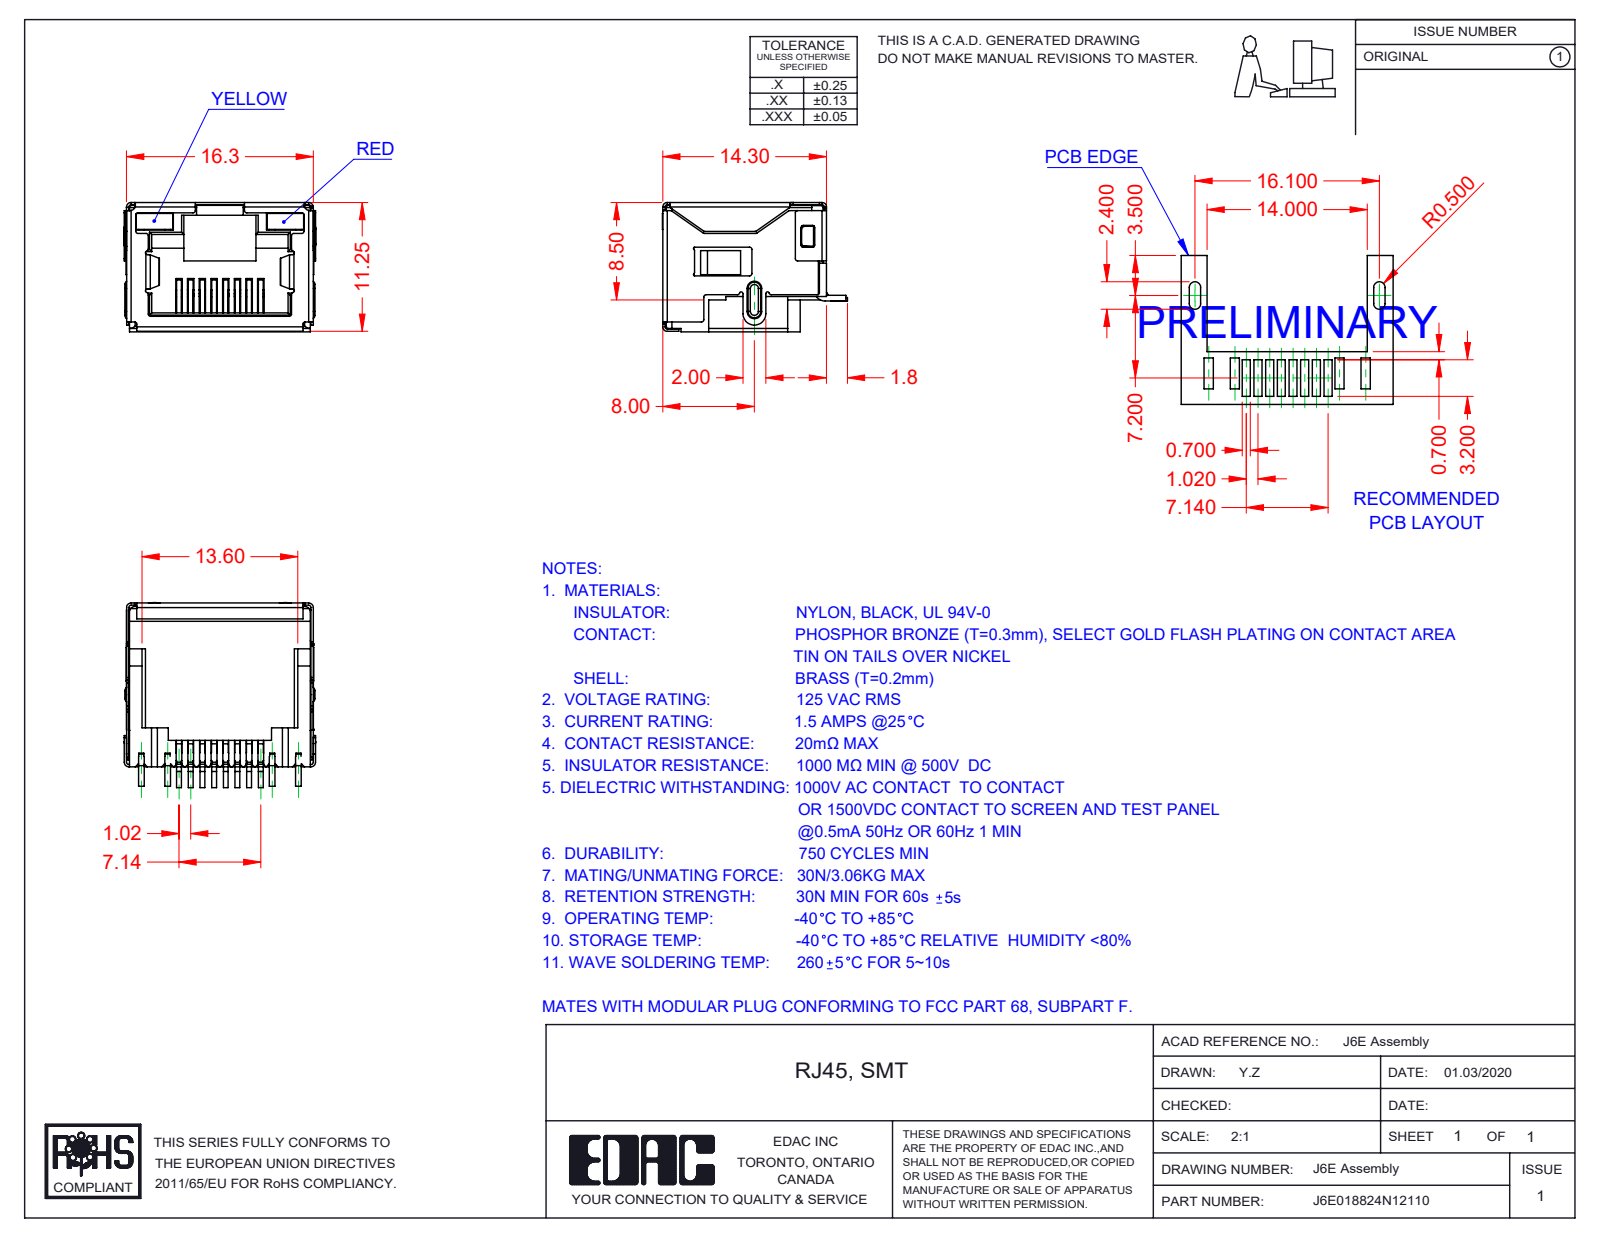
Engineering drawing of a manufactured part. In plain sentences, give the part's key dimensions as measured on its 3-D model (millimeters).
The part is named "6E Shield_LED; 6E LED RH_2-Red; 6E Contacts; J6E018824N12110 (+2 more)". Its 3-D file was written by "SolidWorks 2016 (CONFIG_CONTROL_DESIGN)". It is 12 solids with 1496 faces: 1099 planar, 347 cylindrical and 50 other. Overall it measures 16.75 by 16.15 by 11.3 millimeters. Its volume is 1 109 cubic millimeters and its surface area 4 045 square millimeters. Partial cylindrical surfaces (rounded edges, fillets, slot ends): 82 of radius 0.2, 17 of radius 0.25, 13 of radius 0.4, 13 of radius 0.5, 10 of radius 0.1, 7 of radius 0.15, 4 of radius 0.3, 3 of radius 1. The main face-to-face distances are 11.05, 16.05, 16.1, 15.85, 11.1, 11.3, 2.4, 0.7, 9.85, 0.49.
